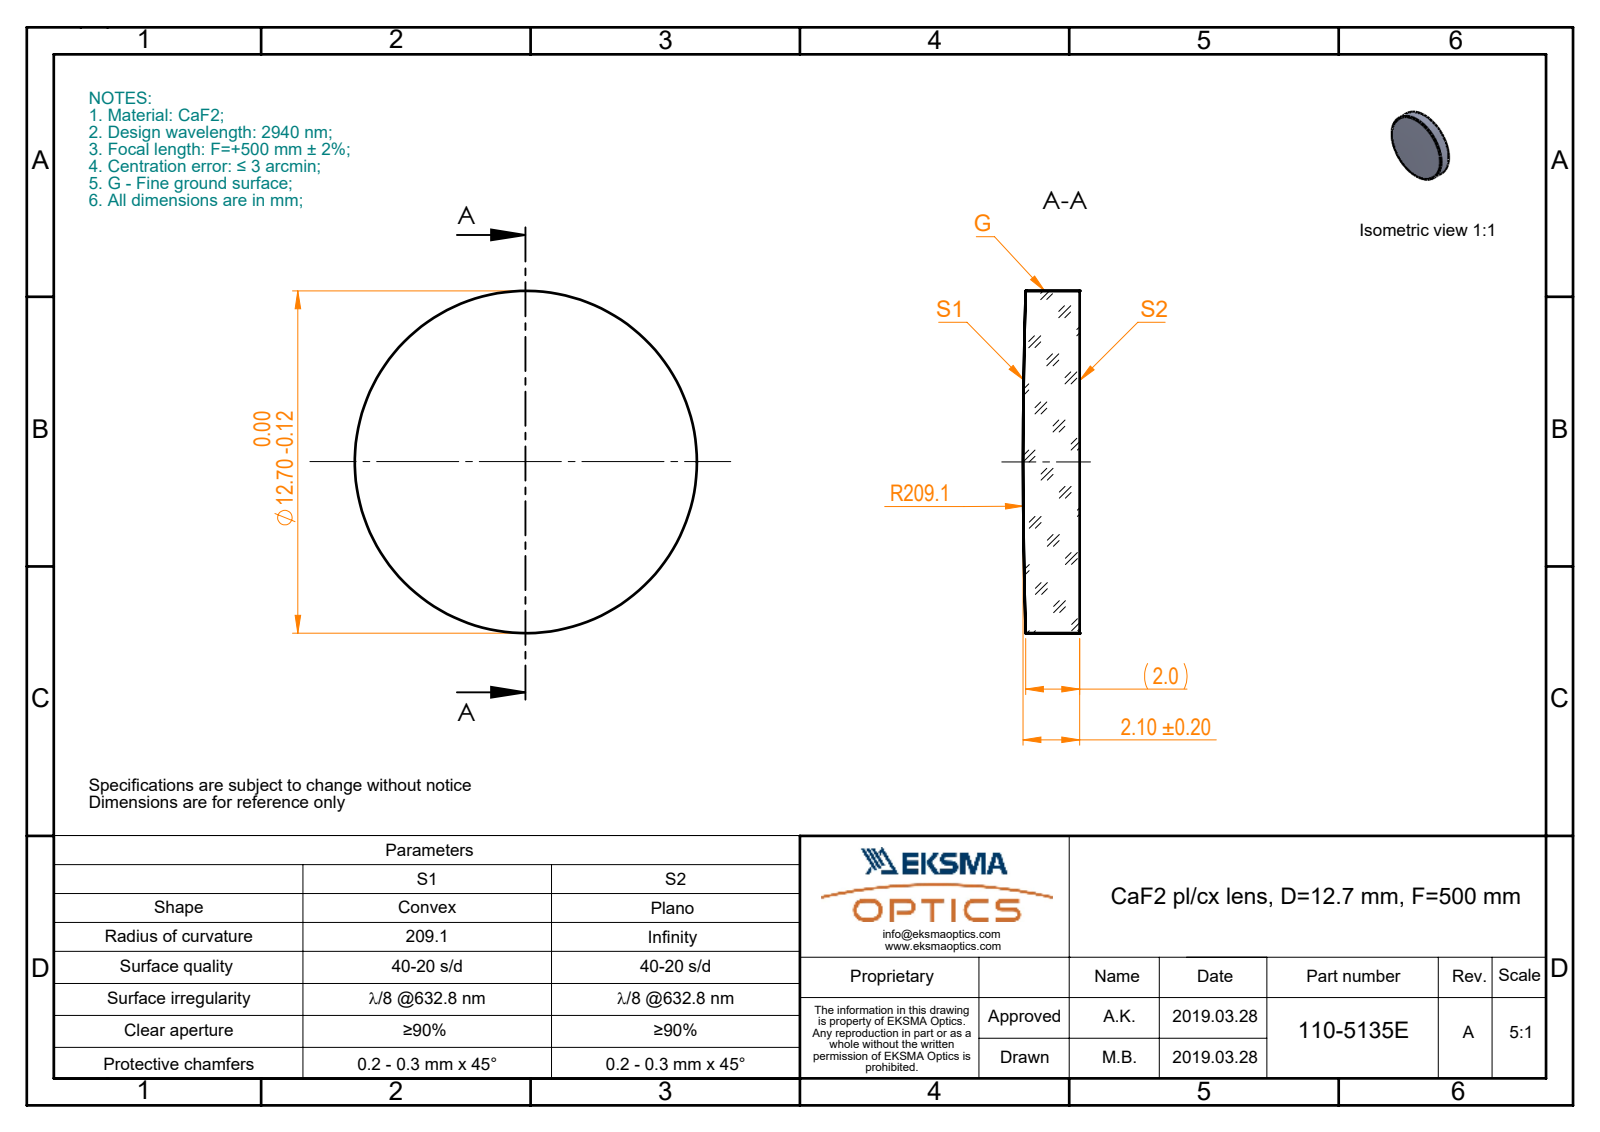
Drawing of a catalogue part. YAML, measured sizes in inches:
part_name: "110-5135E CaF2 pl-cx 12.7 F500"
step_written_by: "SolidWorks 2017 (CONFIG_CONTROL_DESIGN)"
units: inches
bodies: {solids: 1, faces: 5, planar: 1, cylindrical: 2, other: 2}
overall_size: [0.5, 0.5, 0.083]
volume: 0.016
surface_area: 0.516
round_bosses_or_shafts:
  - {diameter: 0.5, count: 1}
